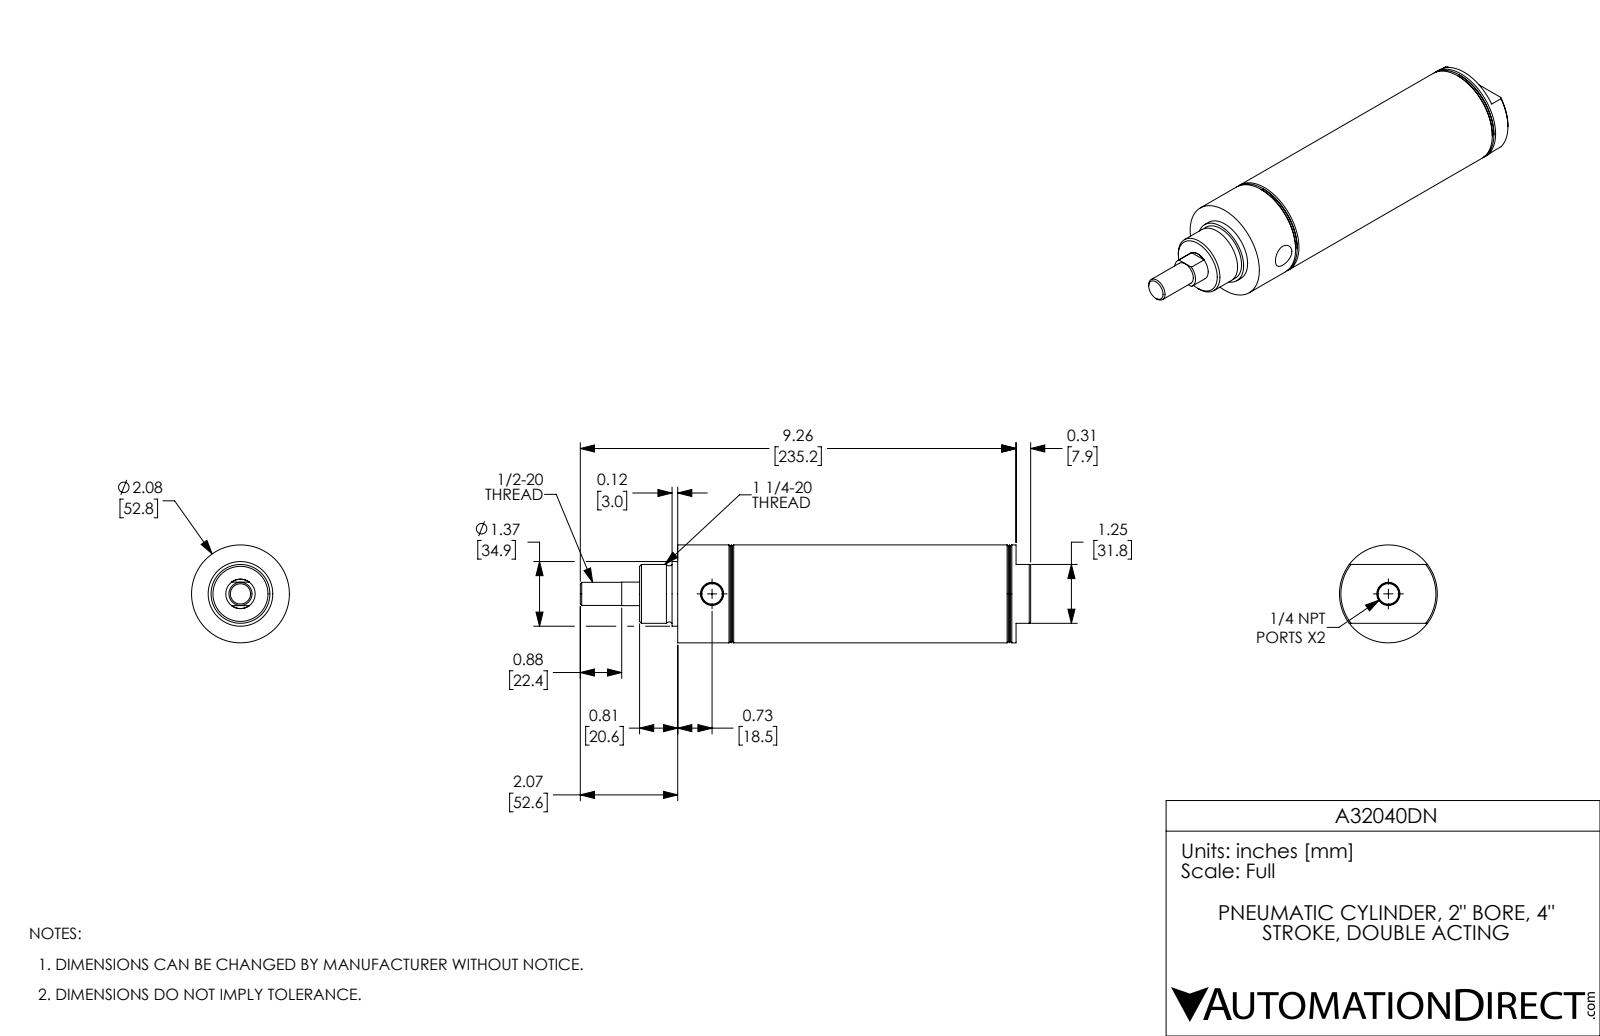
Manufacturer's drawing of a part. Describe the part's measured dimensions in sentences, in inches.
The part is named "A32040DN-MainBody; A32040DN-Rod; A32040DN". Its 3-D file was written by "SolidWorks 2017 (AUTOMOTIVE_DESIGN)". It is 2 solids with 77 faces: 20 planar, 24 cylindrical and 33 other. Overall it measures 9.57 by 2.08 by 2.08 inches. Its volume is 14.87 cubic inches and its surface area 123.4 square inches. Round holes: 2 of diameter 0.438, 1 of diameter 0.625, 1 of diameter 2. Round bosses or shafts: 1 of diameter 2.08, 1 of diameter 1.373, 1 of diameter 1.25, 1 of diameter 0.491. The main face-to-face distances are 1.5, 6, 0.5, 4.5, 4, 2, 7.5, 5.5, 0.31, 1.19.
